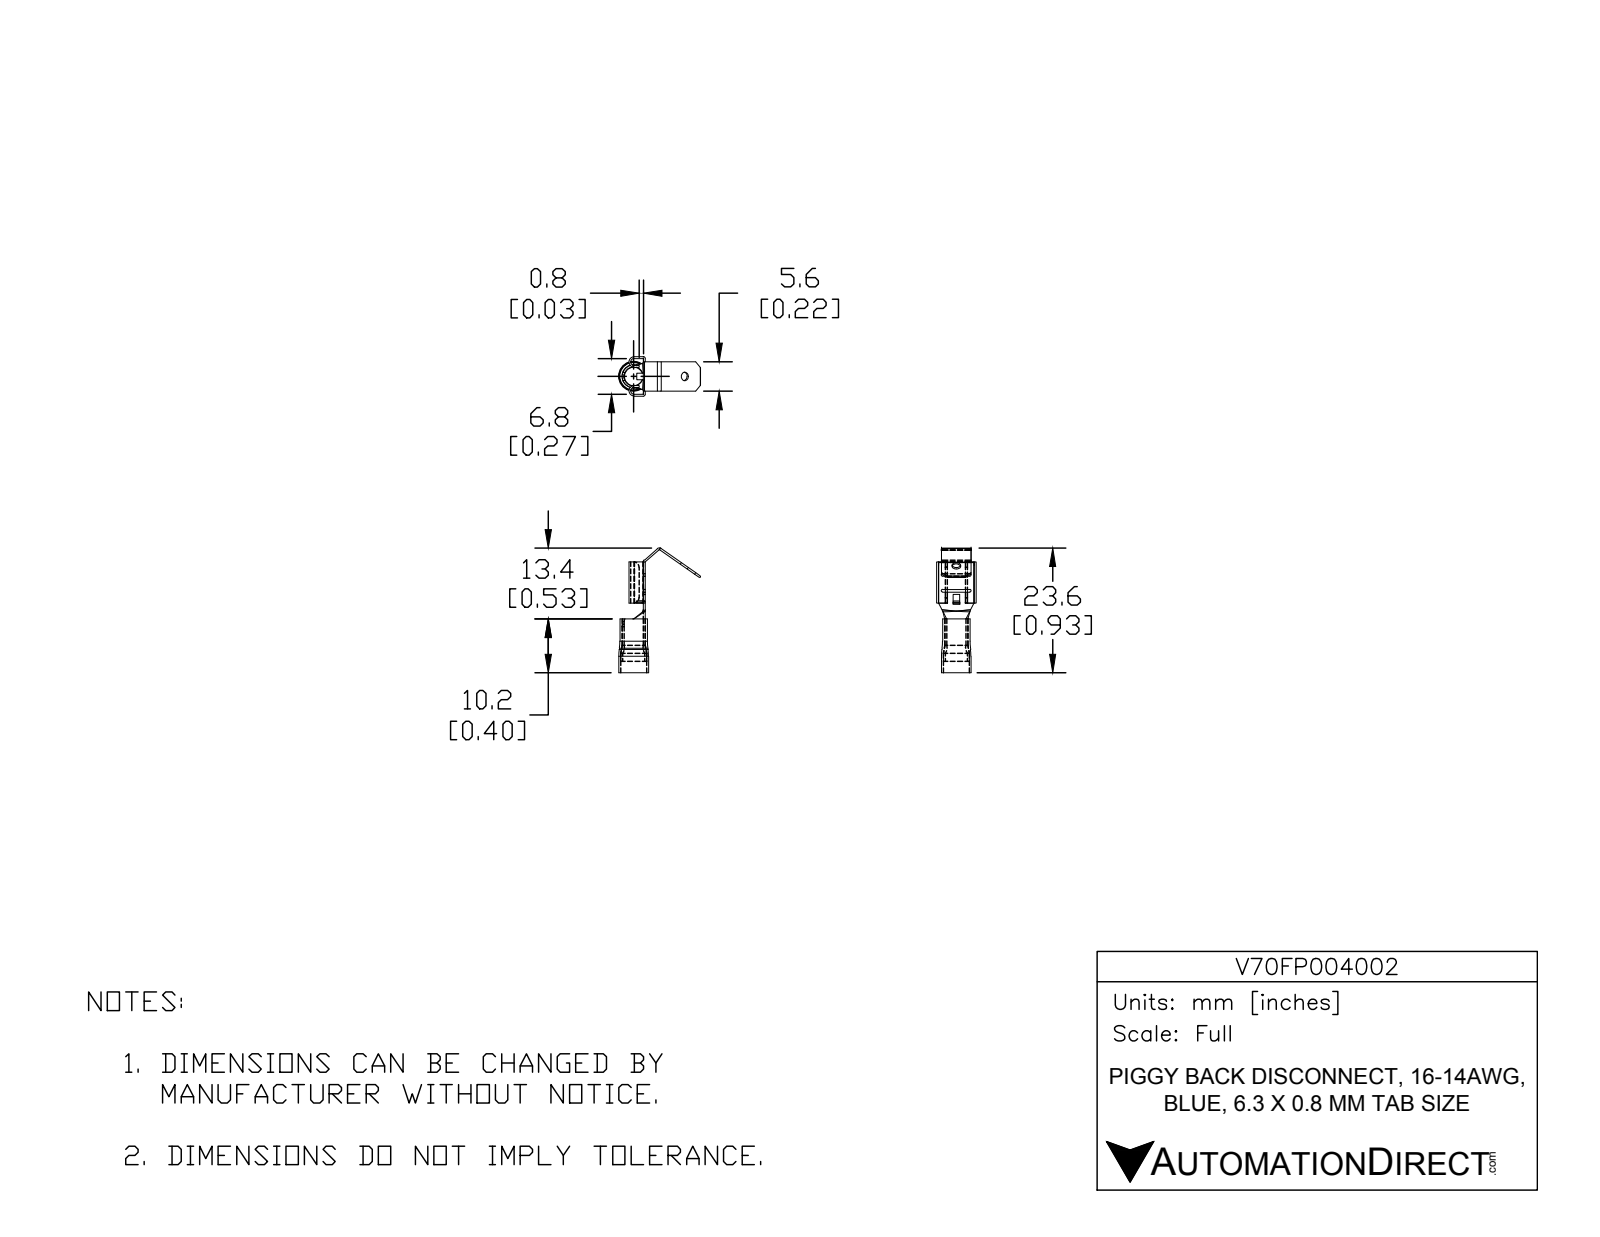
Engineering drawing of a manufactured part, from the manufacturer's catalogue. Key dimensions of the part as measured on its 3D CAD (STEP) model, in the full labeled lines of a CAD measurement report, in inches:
Part name (STEP PRODUCT): V70FP004002
STEP written by: SolidWorks 2017 (AUTOMOTIVE_DESIGN)
Units: inches
Bodies: 2 solids, 123 faces (49 planar, 50 cylindrical, 24 other)
Overall size (bounding box): 0.929 × 0.608 × 0.294
Volume: 0.011 in³ · Surface area: 1.59 in²
Round holes (diameter × count): ⌀0.063 ×1, ⌀0.144 ×1, ⌀0.165 ×1, ⌀0.171 ×1, ⌀0.193 ×1
Round bosses / shafts (diameter × count): ⌀0.22 ×1, ⌀0.205 ×1
Partial cylindrical surfaces — rounded edges, fillets, slot ends (radius × count): R0.01 ×8, R0.02 ×4, R0.039 ×4, R0.015 ×2, R0.024 ×2, R0.026 ×2
Main face-to-face distances: 0.014, 0.065, 0.215, 0.28, 0.079, 0.229, 0.051, 0.201, 0.15, 0.266
